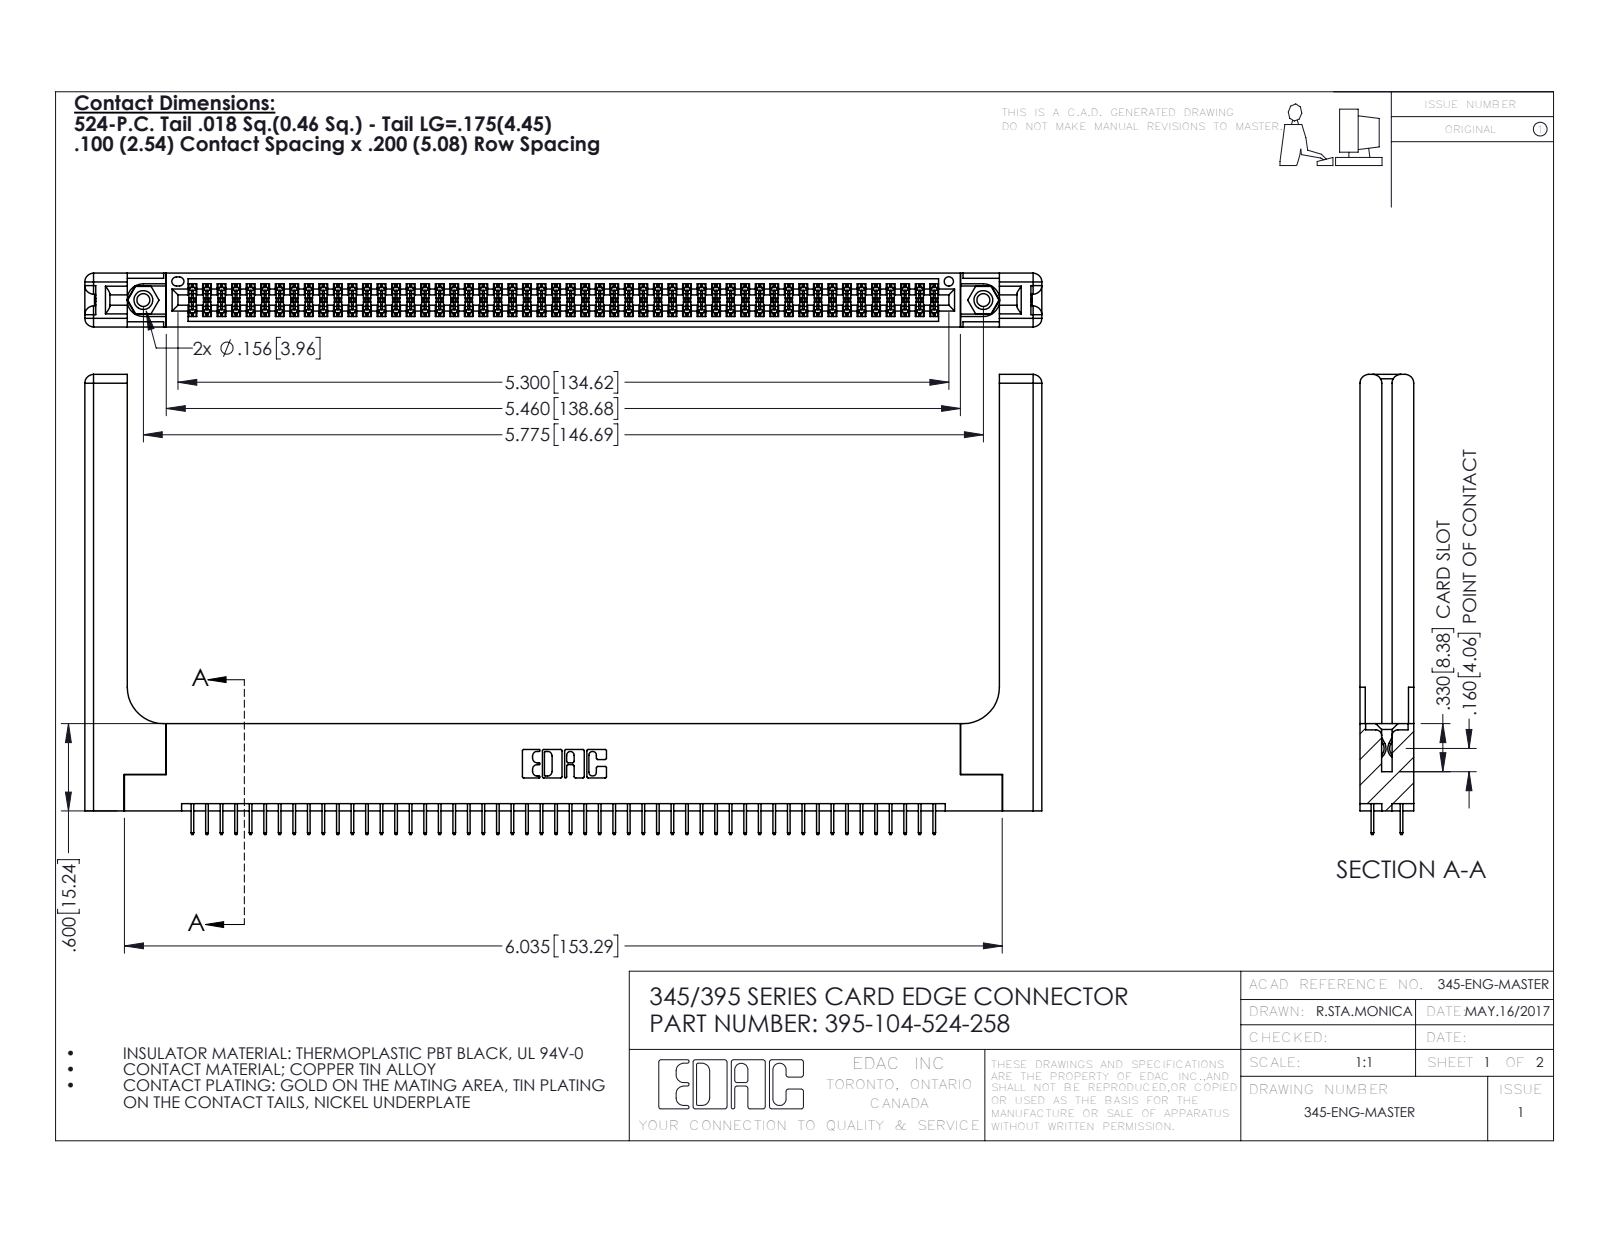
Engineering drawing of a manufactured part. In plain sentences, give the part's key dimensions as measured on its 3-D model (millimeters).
The part is named "345-292-001_345-293-124; 345-220-058_345-220-058; 345 Part_Flush Mounting Lugs - 0.156 Dia-TH; 345-250-001_345-250-001-102 (+1 more)". Its 3-D file was written by "SolidWorks 2016 (CONFIG_CONTROL_DESIGN)". It is 109 solids with 5998 faces: 4284 planar, 1654 cylindrical and 60 other. Overall it measures 167.1 by 80.3 by 9.4 millimeters. Its volume is 24 650 cubic millimeters and its surface area 28 740 square millimeters. Round holes: 2 of diameter 2.3, 2 of diameter 3.2, 2 of diameter 4, 1 of diameter 1.6. Round bosses or shafts: 2 of diameter 3.9. Partial cylindrical surfaces (rounded edges, fillets, slot ends): 156 of radius 0.2, 22 of radius 0.3, 16 of radius 1.5, 6 of radius 0.2, 6 of radius 0.8, 3 of radius 0.7, 2 of radius 0.4, 2 of radius 0.5. The main face-to-face distances are 1.8, 9.4, 7.6, 5.1, 2.5, 6.9, 0.6, 5.7, 3.8, 3.8. The hole center spacings are 6.9, 140.7, 146.7.
